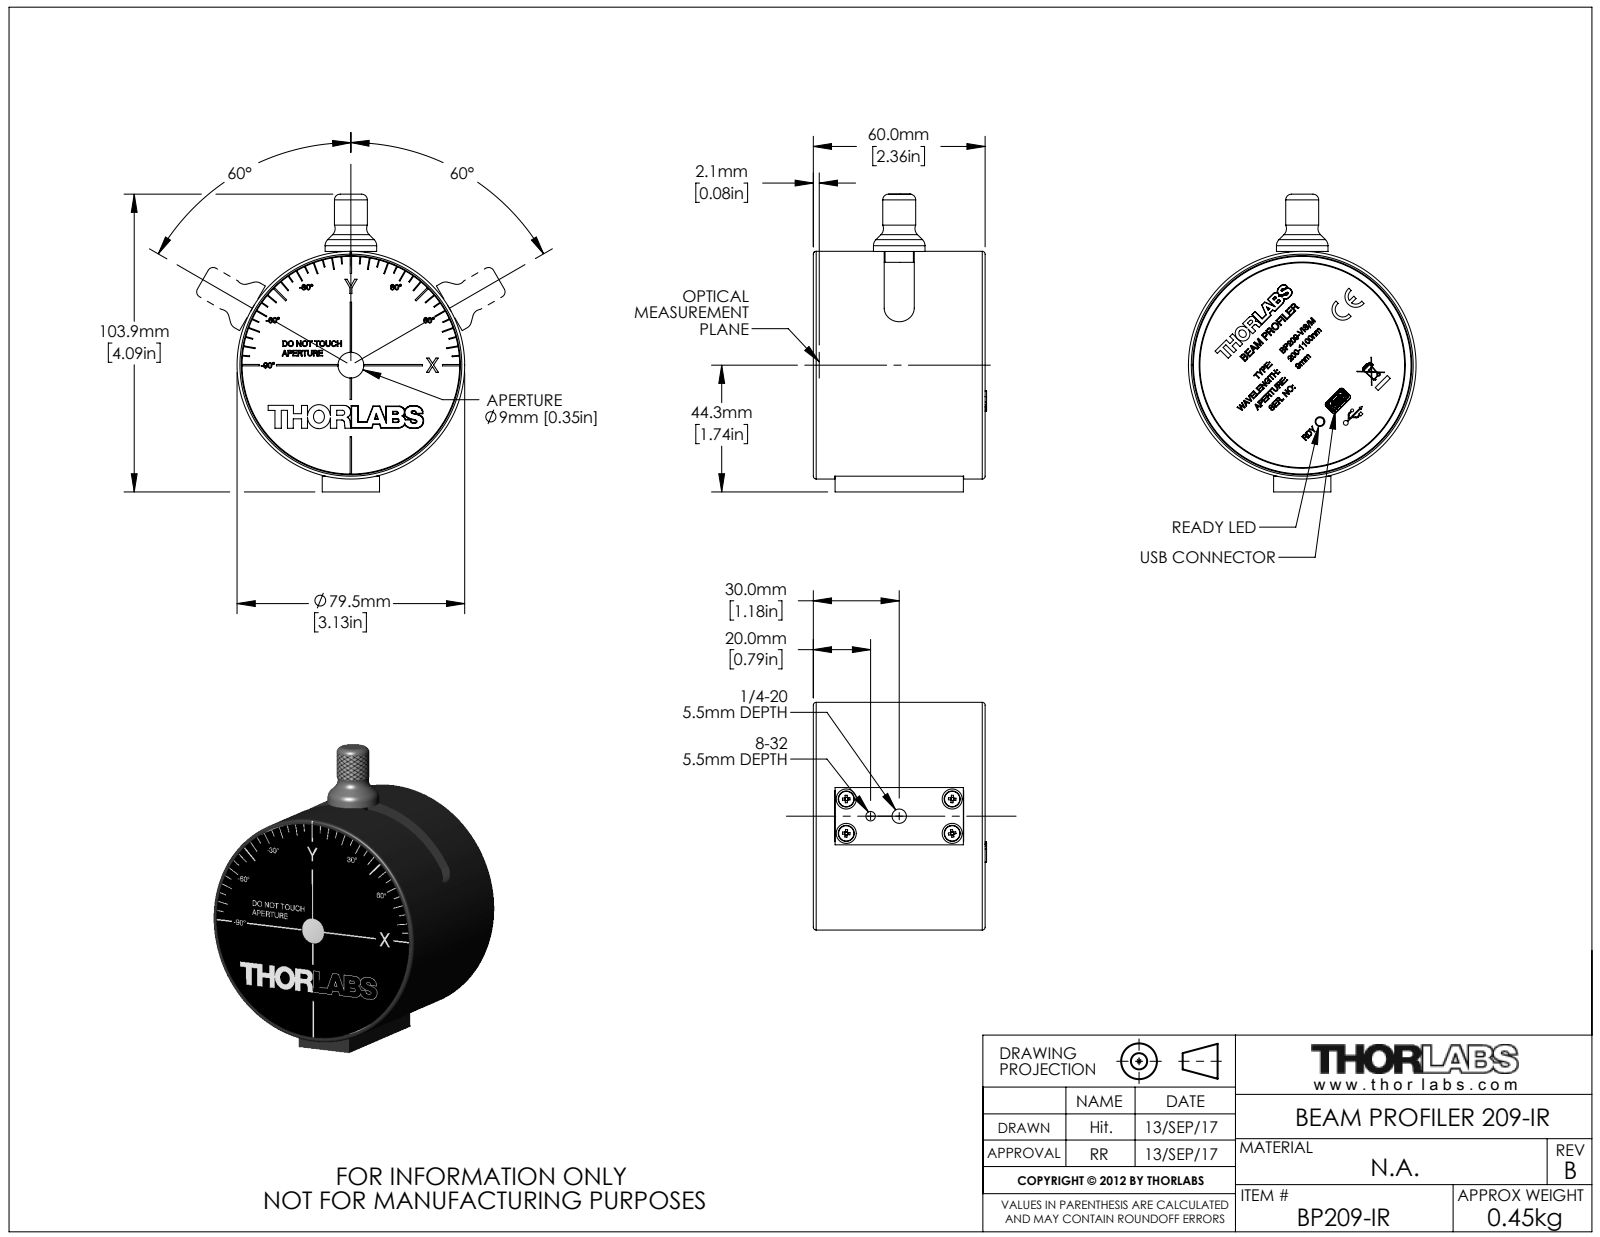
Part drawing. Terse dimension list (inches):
name: 21425-E0W
written by: SolidWorks 2012 (CONFIG_CONTROL_DESIGN)
unit: in
bodies: 14 solids, 3699 faces (2594 planar, 408 cylindrical, 697 other)
size: 4.093 × 3.13 × 2.382
volume: 6.005 in³; area: 153.8 in²
holes: 10× ⌀0.126, 9× ⌀0.087, 8× ⌀0.315, 6× ⌀0.063, 6× ⌀0.248, 5× ⌀0.197, 5× ⌀0.276, 4× ⌀0.098, 4× ⌀0.209, 1× ⌀0.039, 1× ⌀0.051, 1× ⌀0.066
bosses: 4× ⌀0.22, 4× ⌀0.118, 2× ⌀0.031, 1× ⌀3.13, 1× ⌀2.992, 1× ⌀2.839, 1× ⌀2.827, 1× ⌀2.815
rounds: 18× R0.059, 16× R0.157, 14× R0.004, 14× R0.008, 14× R0.039, 9× R0.012, 8× R0.028, 8× R0.197
face distances: 0.039, 2.323, 2.35, 2.362, 2.283, 0.028, 2.311, 0.02, 0.079, 0.059
hole spacings: 0.934, 1.22, 1.726, 2.255, 1.063, 1.841, 1.063, 0.766
